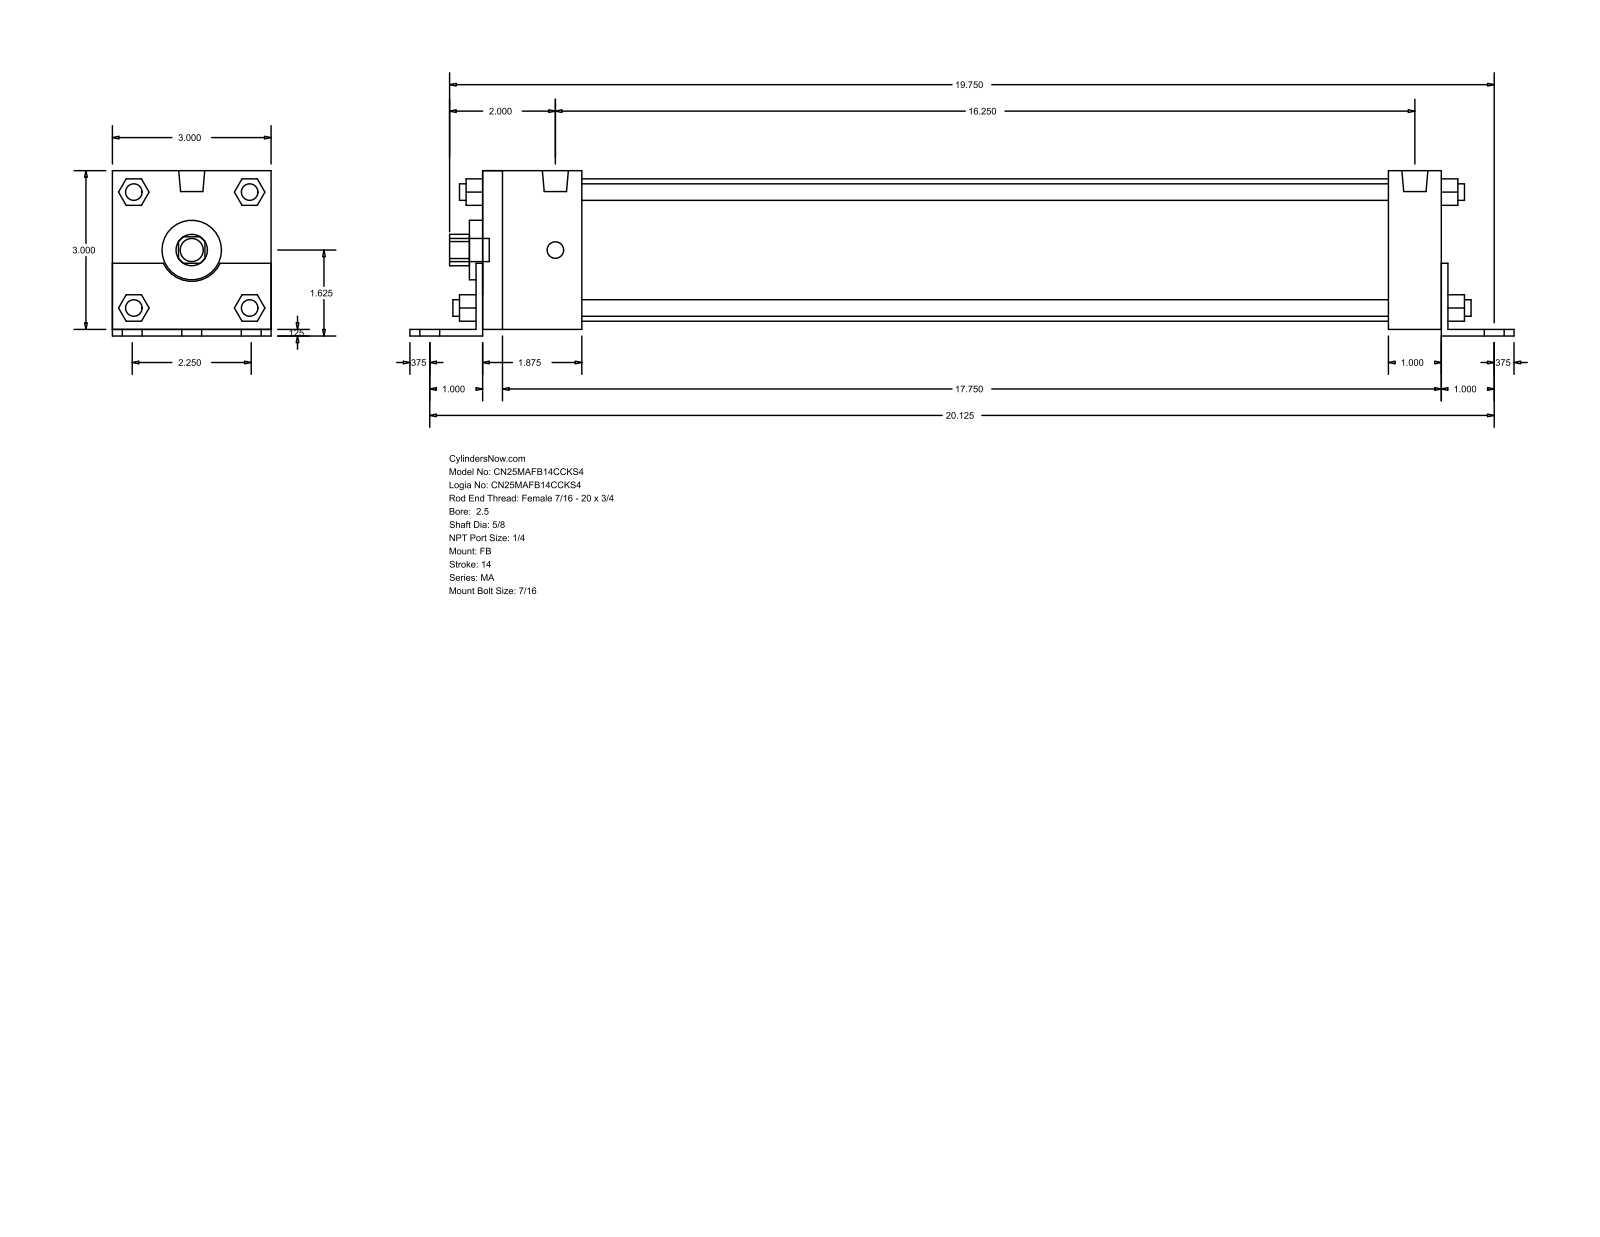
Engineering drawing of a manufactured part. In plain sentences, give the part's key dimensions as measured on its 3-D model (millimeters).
The part is named "MA_FB__0250_0.625". Its 3-D file was written by "GSSL Pune (CONFIG_CONTROL_DESIGN)". It is 0 solids with 140 faces: 105 planar, 35 cylindrical and 0 other. Overall it measures 530.23 by 79.38 by 76.2 millimeters. Round holes: 1 of diameter 15.88, 1 of diameter 28.57, 1 of diameter 68.33. Round bosses or shafts: 8 of diameter 7.94, 7 of diameter 11.11, 2 of diameter 12.49. Partial cylindrical surfaces (rounded edges, fillets, slot ends): 1 of radius 7.54, 1 of radius 15.05. The main face-to-face distances are 76.2, 3.17, 79.37, 3.18, 463.55, 460.37, 28.58, 47.62, 25.4, 466.73.
